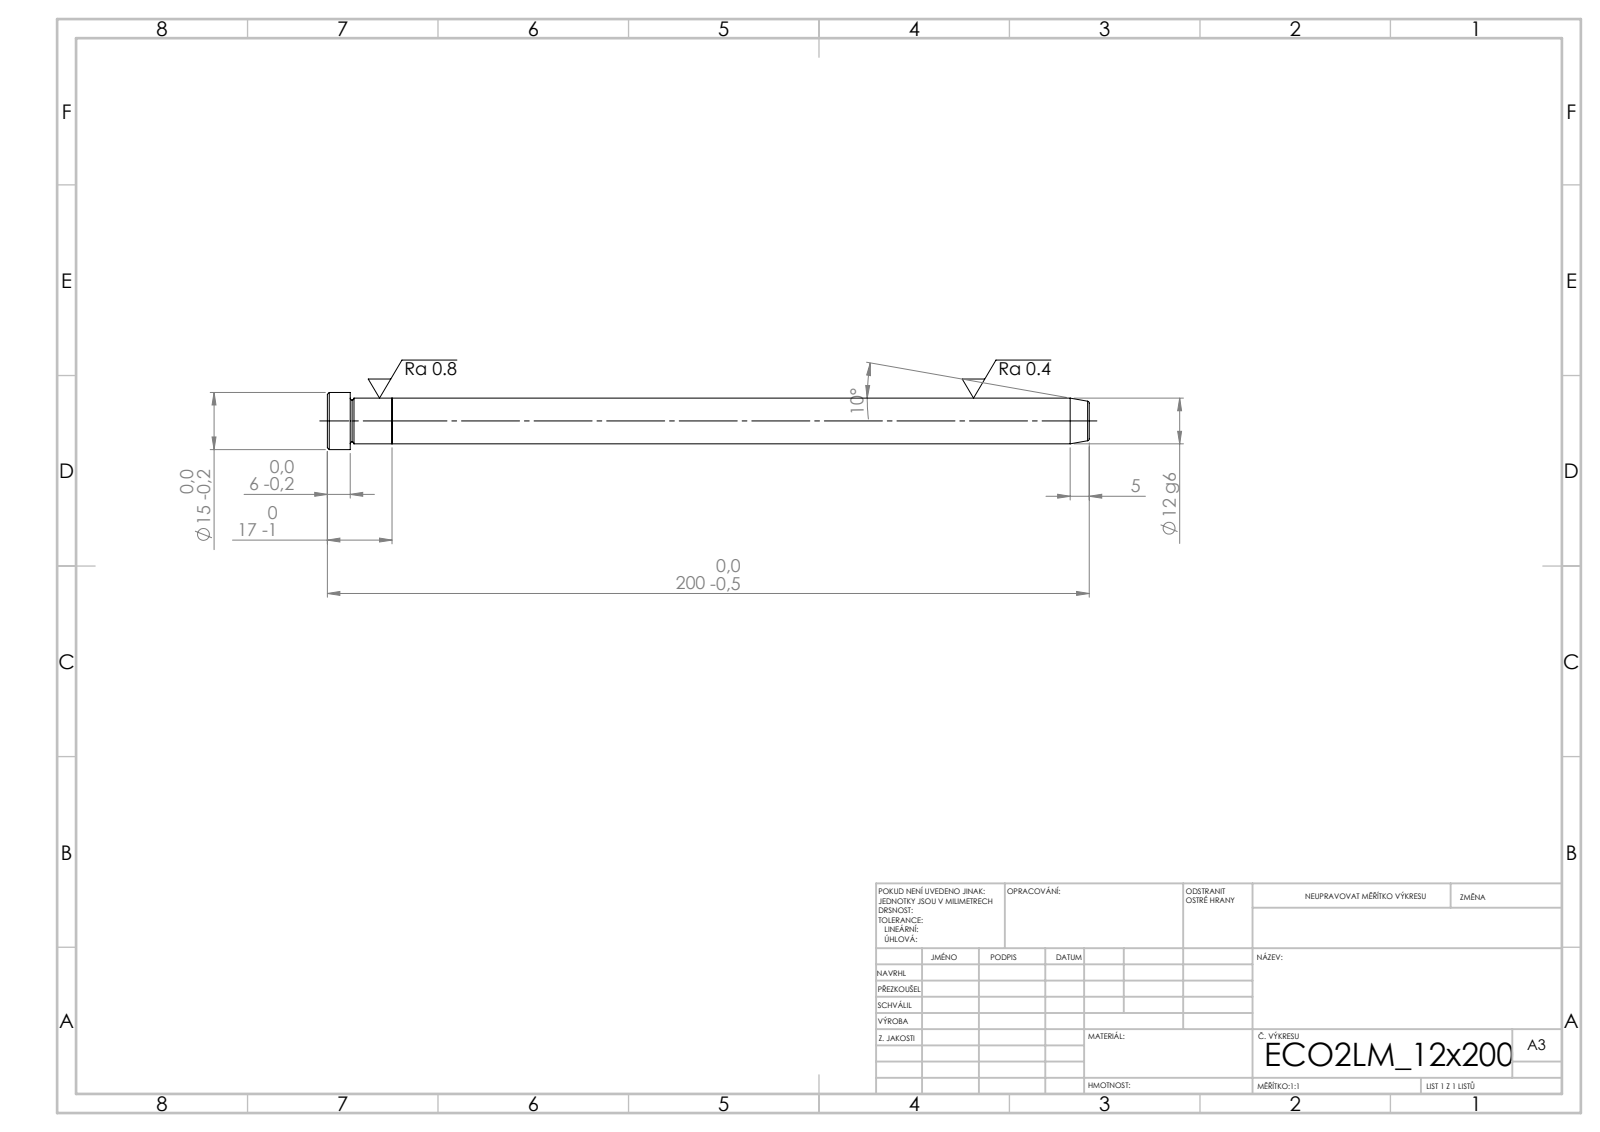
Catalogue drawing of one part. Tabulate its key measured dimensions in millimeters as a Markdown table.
| quantity | value |
| --- | --- |
| STEP written by | SolidWorks 2019 (CONFIG_CONTROL_DESIGN) |
| units | millimeters |
| bodies | 2 solids, 21 faces (5 planar, 6 cylindrical, 10 other) |
| overall size | 200 × 15 × 15 |
| volume | 22 901 mm³ |
| surface area | 8 134 mm² |
| round bosses / shafts (diameter × count) | 15 × 1, 12 × 1 |
| main face-to-face distances | 17, 183, 200, 194, 11, 6 |
